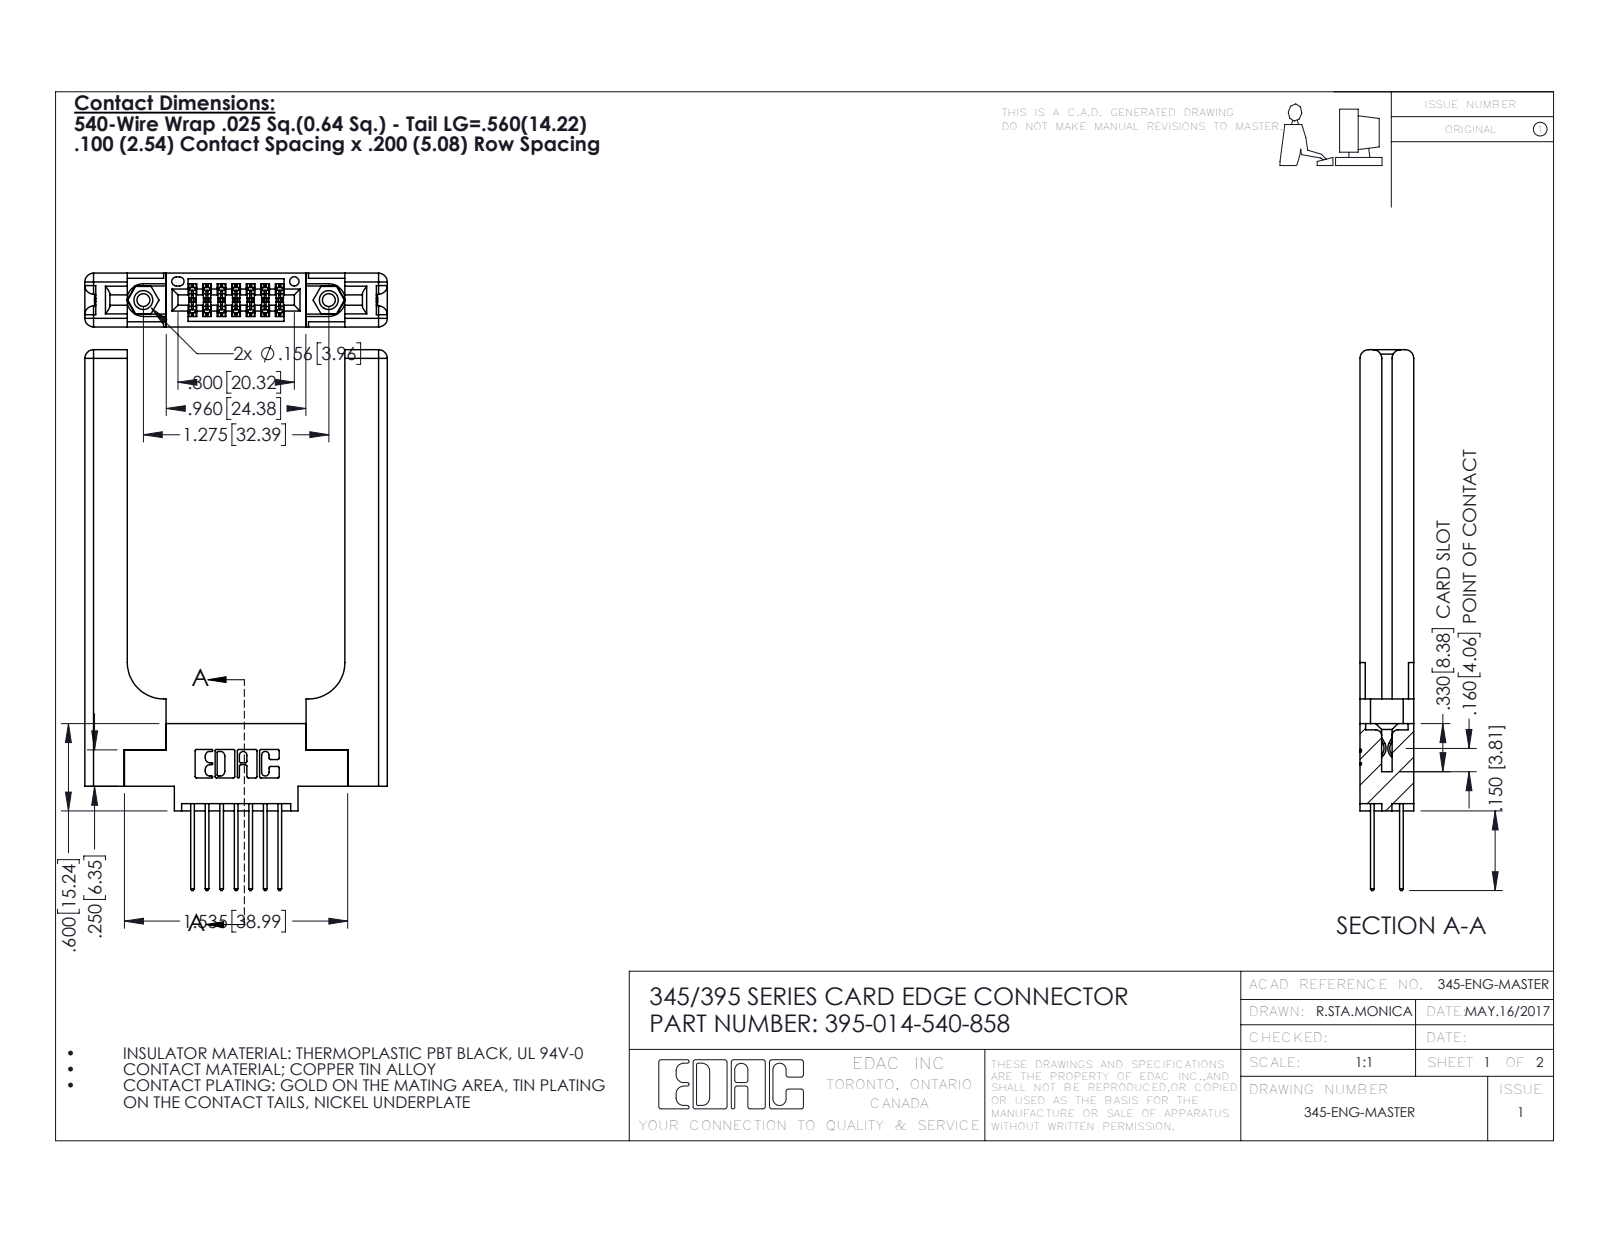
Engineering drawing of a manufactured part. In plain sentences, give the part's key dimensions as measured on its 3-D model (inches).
The part is named "345-250-001_345-250-001-102; 345-220-058_345-220-058; 345-292-001_345-293-140; 345 Part_0.170 Offset - 0.156 Dia-TH (+1 more)". Its 3-D file was written by "SolidWorks 2016 (CONFIG_CONTROL_DESIGN)". It is 19 solids with 1086 faces: 694 planar, 332 cylindrical and 60 other. Overall it measures 3.717 by 2.079 by 0.37 inches. Its volume is 0.807 cubic inches and its surface area 18.27 square inches. Round holes: 2 of diameter 0.089, 2 of diameter 0.125, 2 of diameter 0.156, 1 of diameter 0.064. Round bosses or shafts: 2 of diameter 0.155. Partial cylindrical surfaces (rounded edges, fillets, slot ends): 22 of radius 0.01, 21 of radius 0.006, 16 of radius 0.06, 14 of radius 0.01, 6 of radius 0.007, 6 of radius 0.031, 3 of radius 0.026, 2 of radius 0.014. The main face-to-face distances are 0.37, 0.15, 0.072, 0.22, 0.148, 0.077, 0.298, 1.496, 0.225, 0.071. The hole center spacings are 0.27, 1.045, 1.275.
